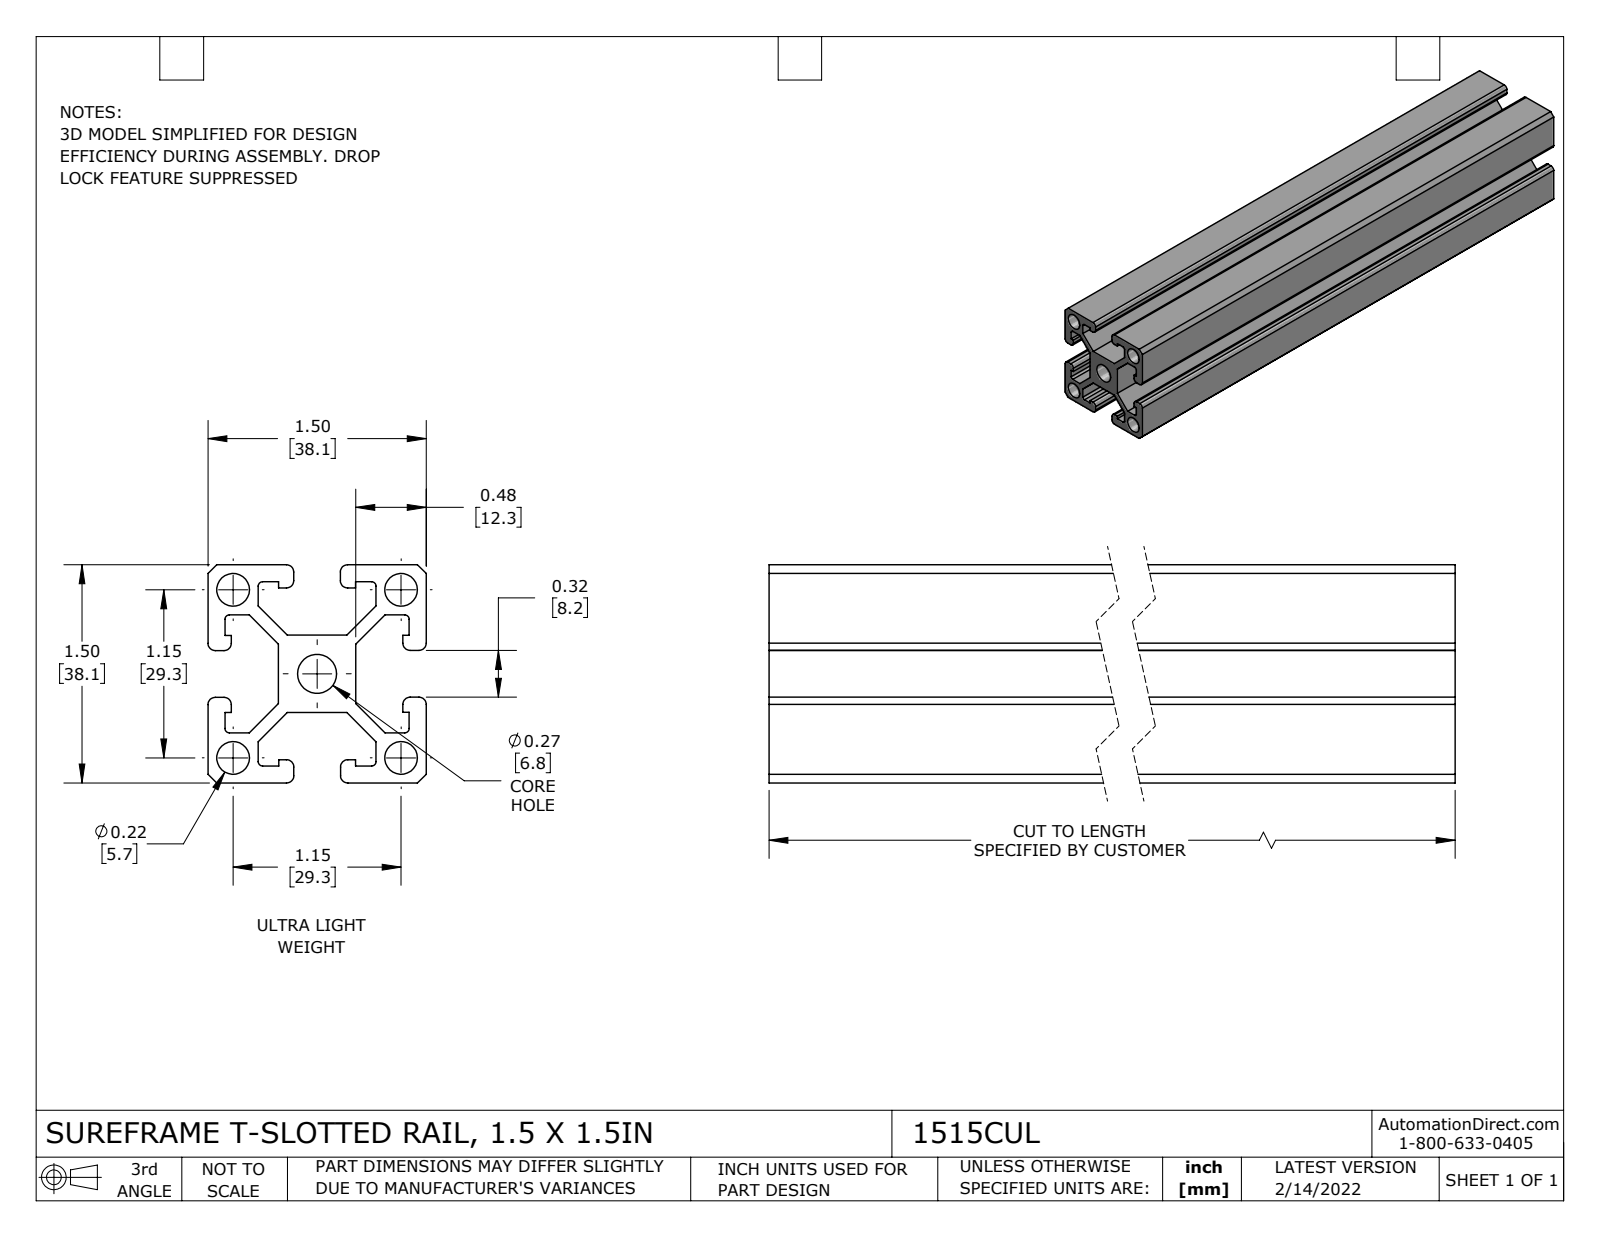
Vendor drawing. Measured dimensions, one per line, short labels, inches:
name: 1515CUL
written by: SolidWorks 2021 (CONFIG_CONTROL_DESIGN)
unit: in
bodies: 1 solid, 100 faces (66 planar, 34 cylindrical, 0 other)
size: 8 × 1.5 × 1.5
volume: 7.016 in³; area: 134.6 in²
holes: 4× ⌀0.225, 1× ⌀0.268
rounds: 16× R0.05, 8× R0.03
face distances: 1.5, 0.484, 1.016, 0.087, 0.345, 1.155, 0.139, 0.671, 0.117, 1.383
hole spacings: 0.817, 1.155, 1.633
